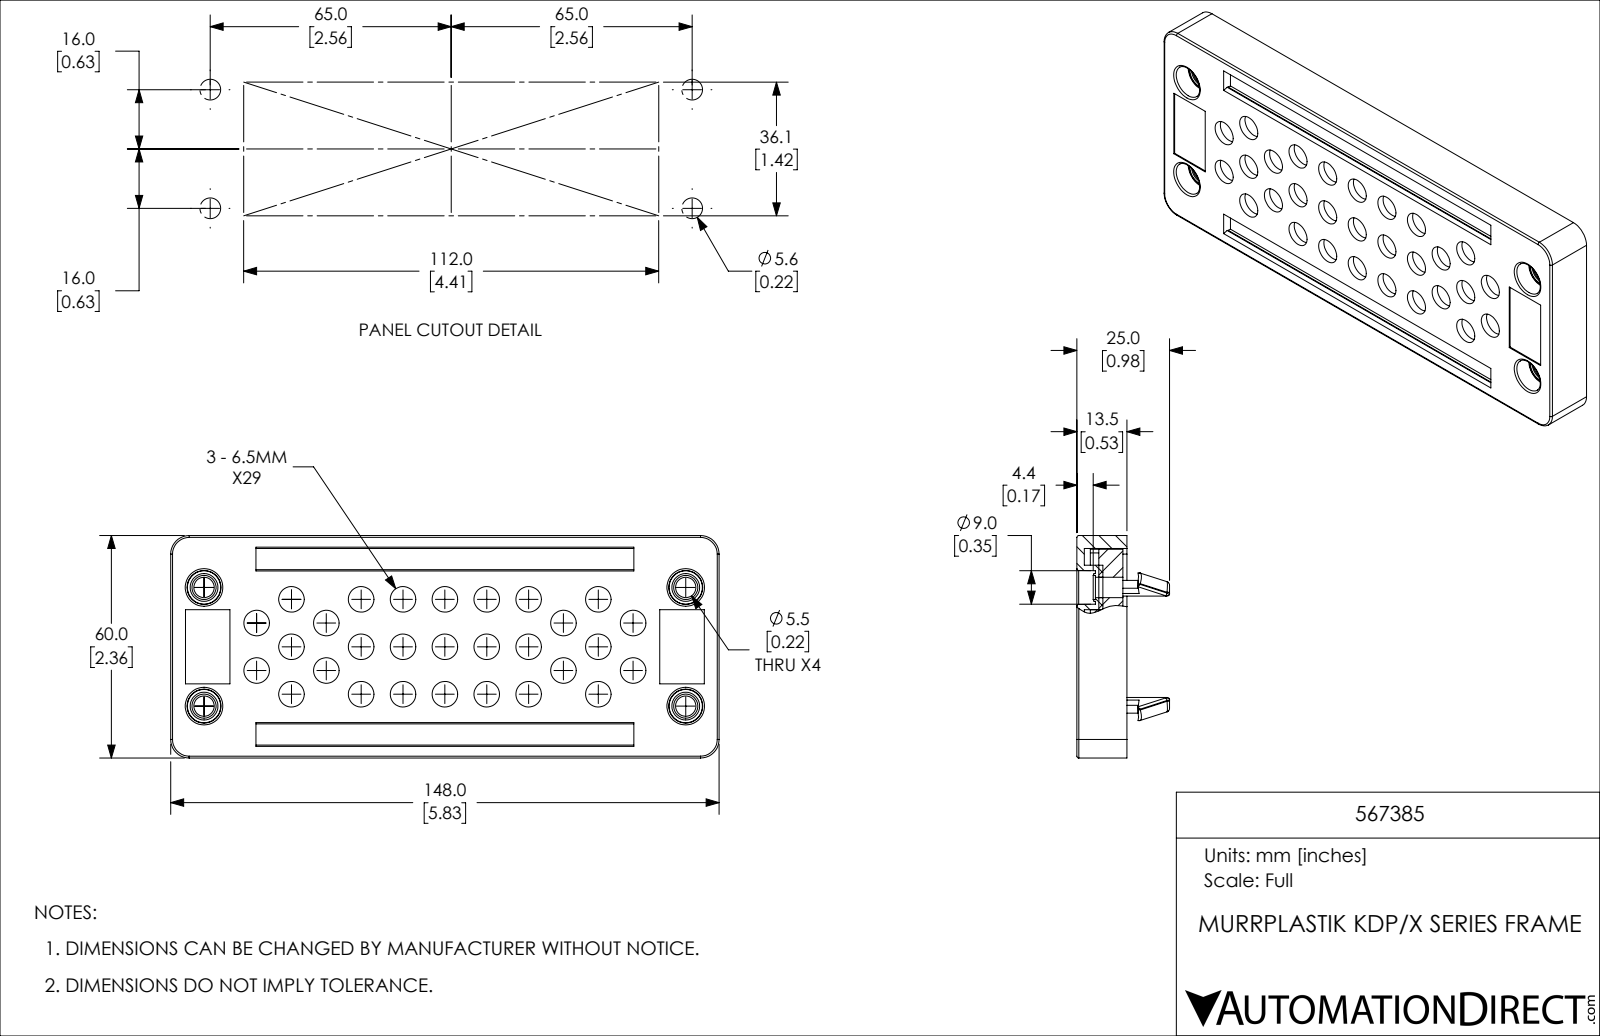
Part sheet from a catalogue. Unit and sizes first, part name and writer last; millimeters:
Units: millimetres
Overall size (bounding box): 148 × 60 × 25
Round holes (diameter × count): ⌀6.9 ×29, ⌀10.3 ×29, ⌀5.5 ×4, ⌀6.5 ×4
Round bosses / shafts (diameter × count): ⌀7.5 ×4
Partial cylindrical surfaces — rounded edges, fillets, slot ends (radius × count): R1 ×28, R3 ×8, R0.5 ×4, R1.5 ×4, R2 ×4, R3.25 ×4, R3.5 ×4, R5 ×4
Main face-to-face distances: 2.3, 5.9, 3.6, 6.5, 8.8, 12.4, 2, 1.6, 3.9, 10.4
Hole centre spacings: 11.37, 12.8, 17.07, 73.68, 11.3, 21.38, 22.74, 25.97
Volume: 78 183 mm³ · Surface area: 62 724 mm²
Bodies: 3 solids, 451 faces (151 planar, 260 cylindrical, 40 other)
Part name (STEP PRODUCT): 567385
STEP written by: SolidWorks 2019 (CONFIG_CONTROL_DESIGN)
